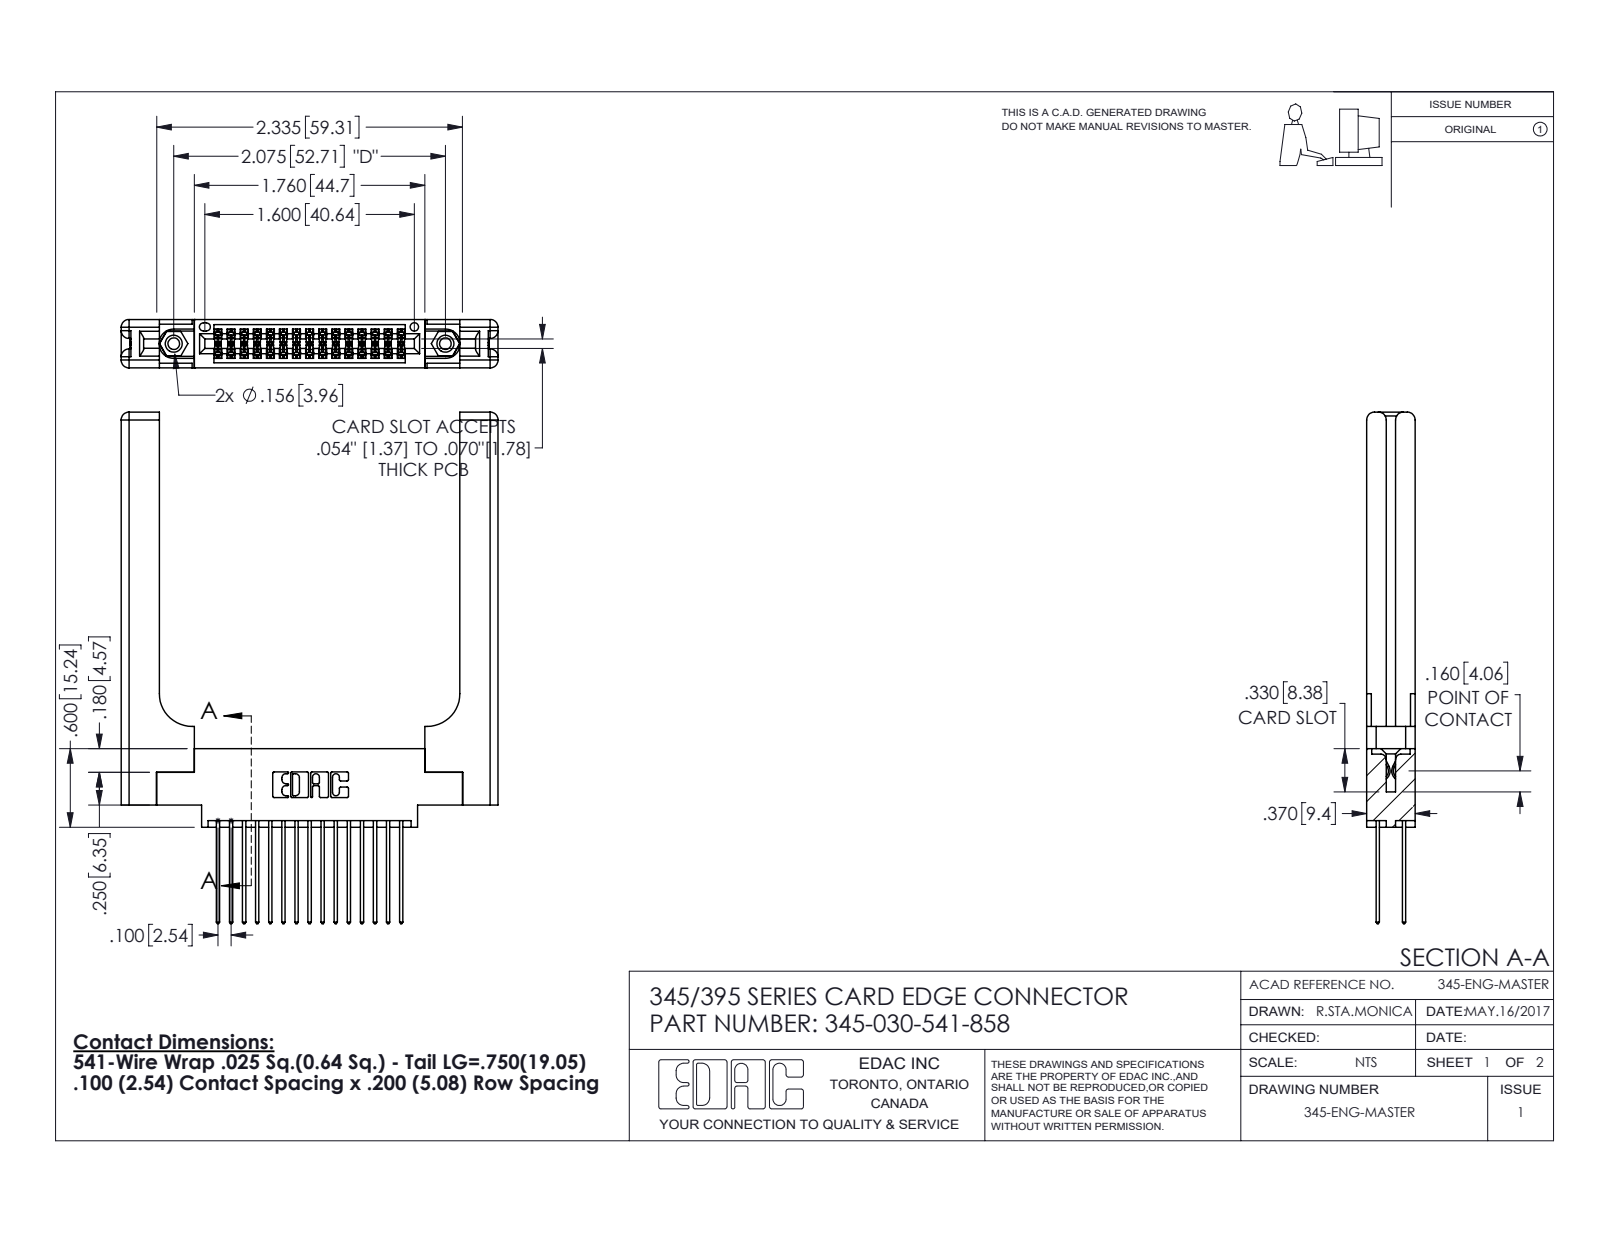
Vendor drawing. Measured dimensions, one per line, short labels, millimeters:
name: 345-250-001_345-250-001-102; 345-030-541-858; 345-220-058_345-220-058; 345-292-001_345-293-141 (+1 more)
written by: SolidWorks 2016 (CONFIG_CONTROL_DESIGN)
unit: mm
bodies: 35 solids, 1886 faces (1222 planar, 604 cylindrical, 60 other)
size: 99.2 × 73.1 × 9.4
volume: 15 400 mm³; area: 15 700 mm²
holes: 2× ⌀2.3, 2× ⌀3.2, 2× ⌀4, 1× ⌀1.6
bosses: 2× ⌀3.9
rounds: 45× R0.2, 30× R0.3, 22× R0.3, 16× R1.5, 6× R0.2, 6× R0.8, 3× R0.7, 2× R0.4
face distances: 9.4, 1.8, 7.6, 2.5, 6.9, 0.6, 5.1, 3.8, 3.8, 2
hole spacings: 6.9, 46.8, 52.7
